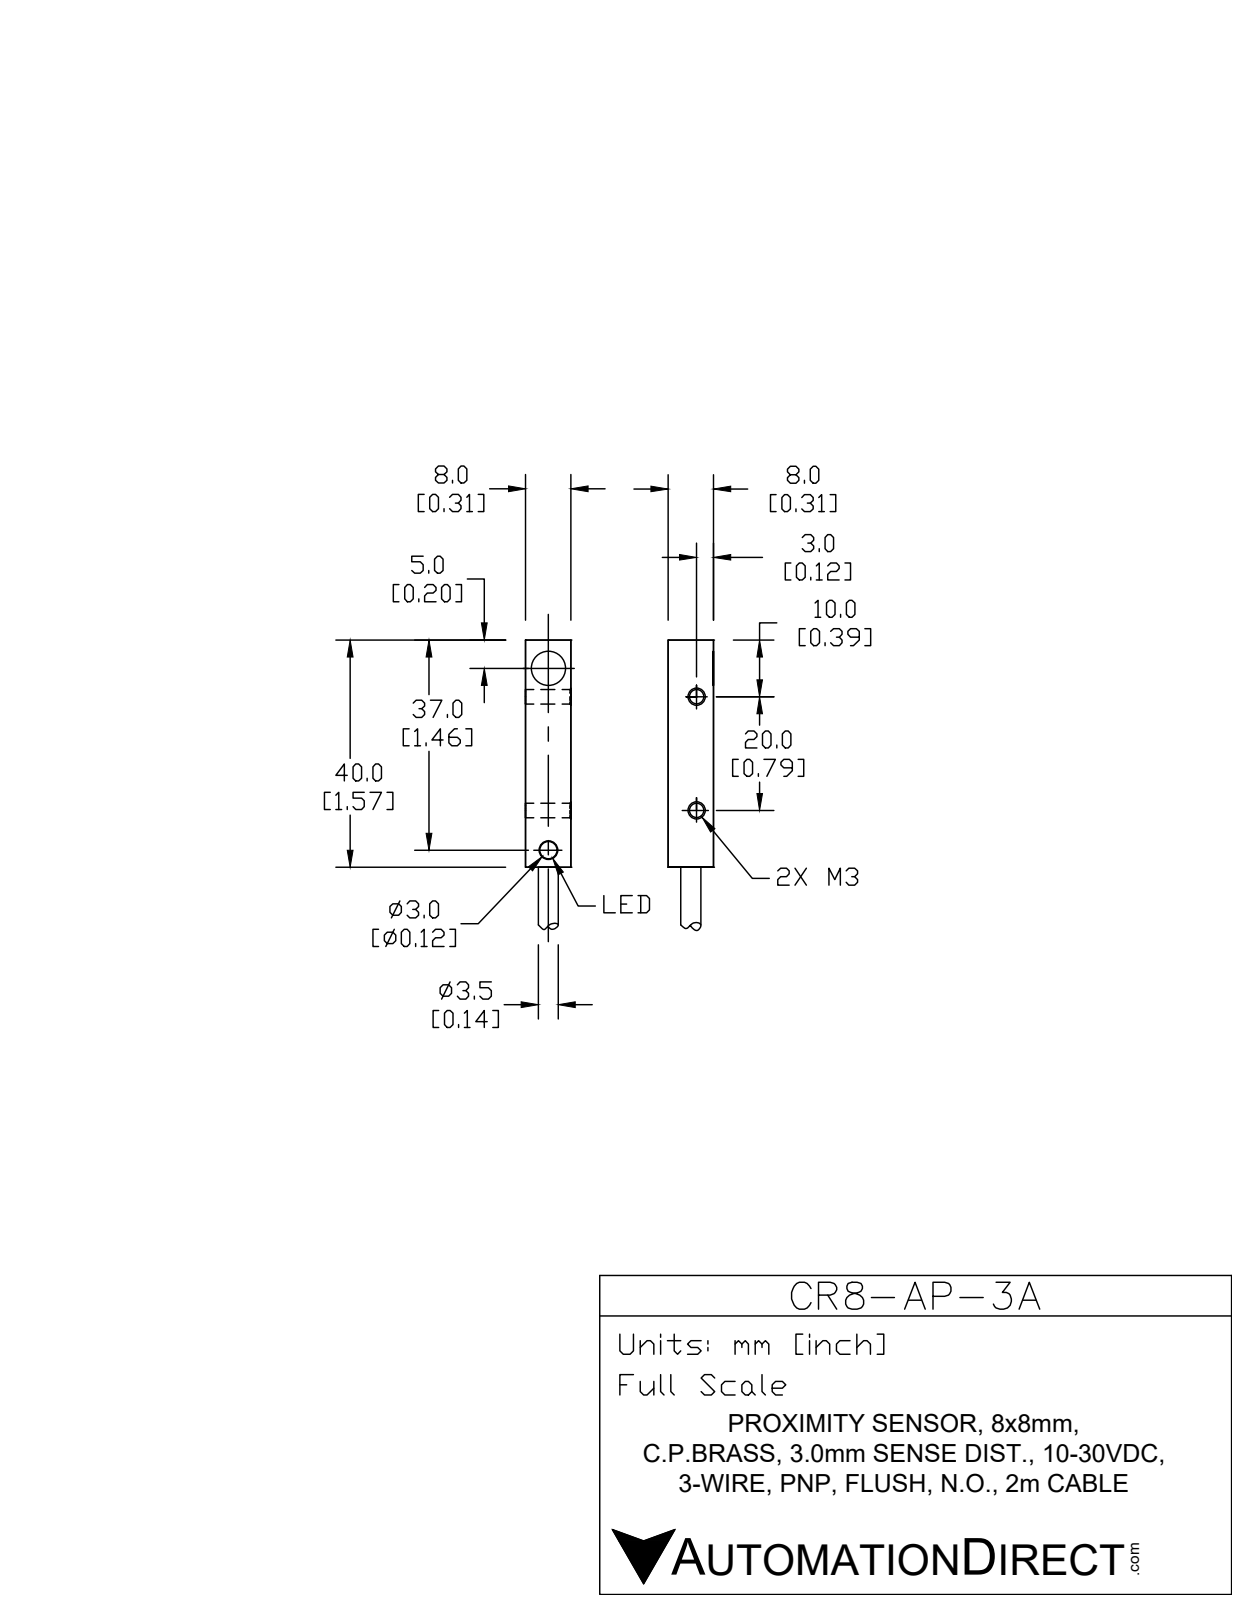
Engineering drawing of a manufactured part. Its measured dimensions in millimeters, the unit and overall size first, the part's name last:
Units: millimetres
Overall size (bounding box): 62.9 × 8 × 8
Round holes (diameter × count): ⌀2.5 ×2
Round bosses / shafts (diameter × count): ⌀3.5 ×1
Main face-to-face distances: 8, 40, 7.9
Hole centre spacings: 20
Volume: 2 690 mm³ · Surface area: 1 757 mm²
Bodies: 1 solid, 16 faces (7 planar, 3 cylindrical, 6 other)
Part name (STEP PRODUCT): CR8-AP-3A
STEP written by: SolidWorks 2017 (AUTOMOTIVE_DESIGN)
